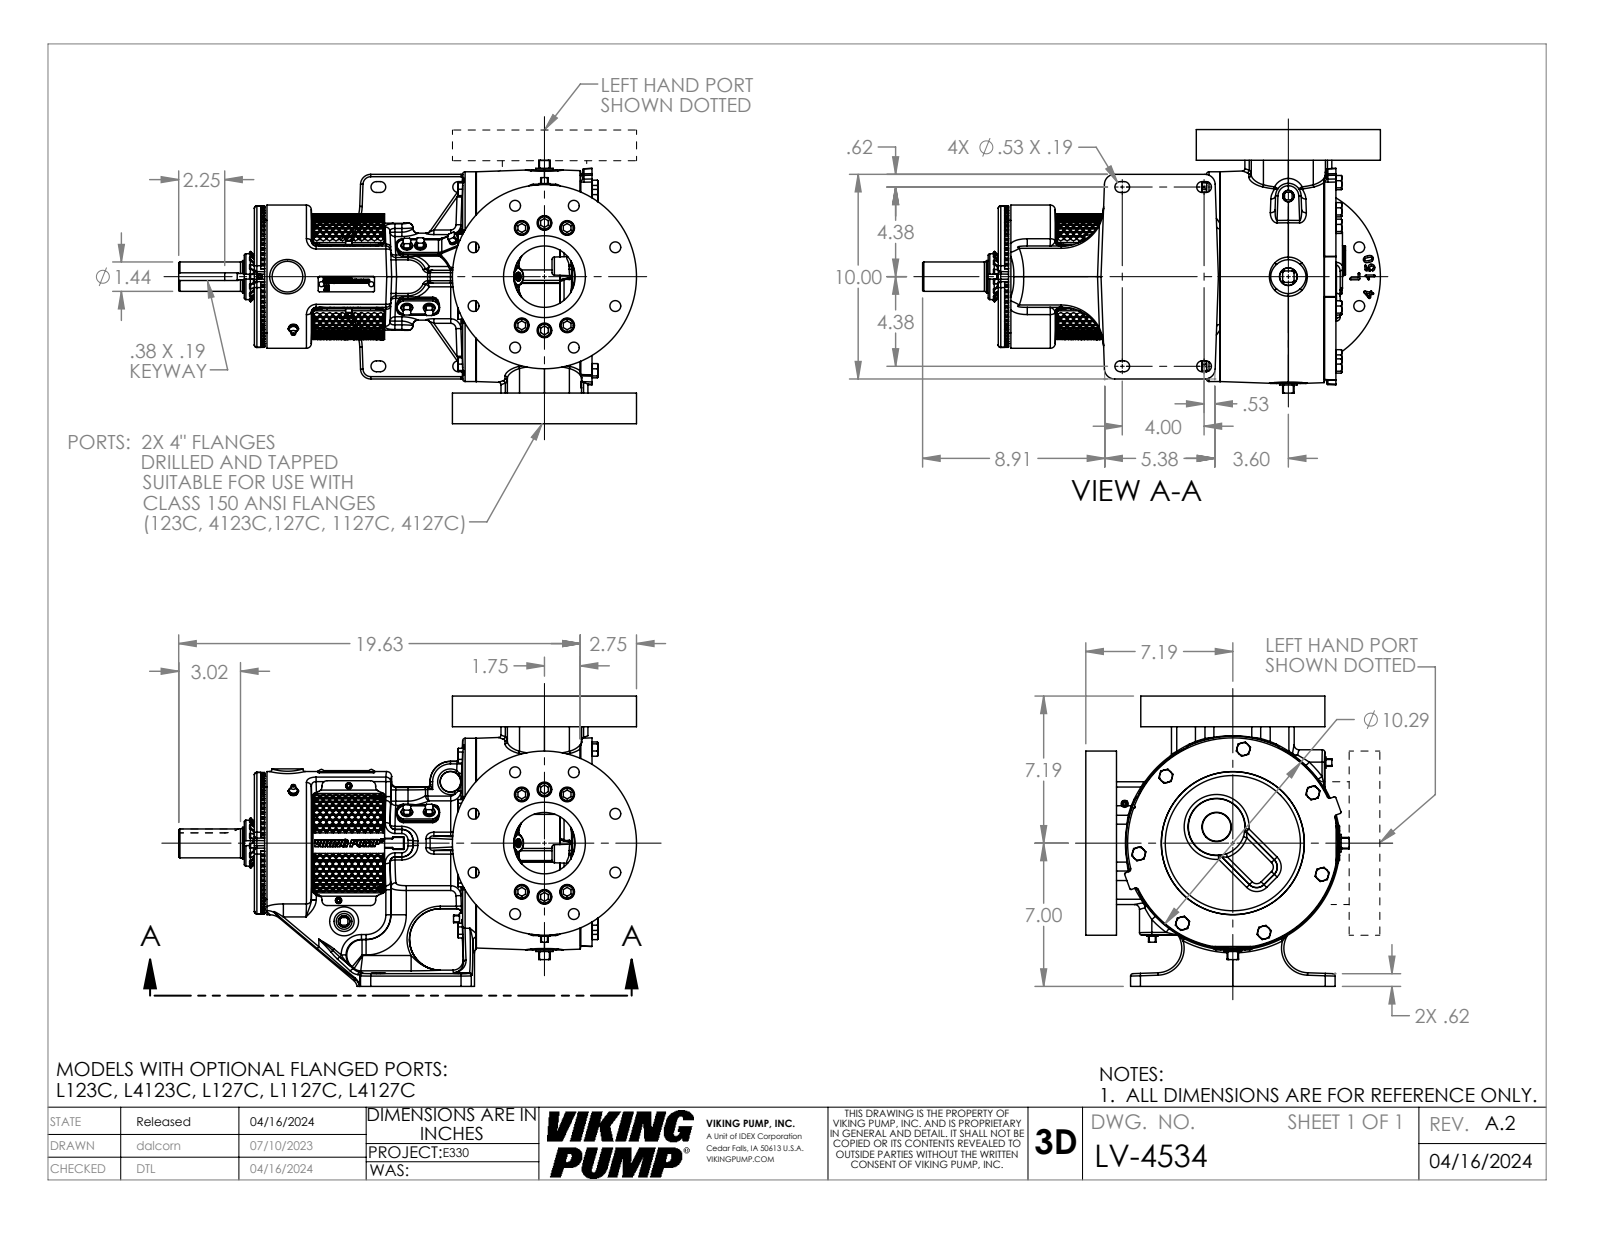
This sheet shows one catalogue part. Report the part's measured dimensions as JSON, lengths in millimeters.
{"part_name": "LV-4534", "step_written_by": "SolidWorks 2022 (AUTOMOTIVE_DESIGN)", "units": "millimeters", "bodies": {"solids": 1, "faces": 4460, "planar": 1526, "cylindrical": 968, "other": 1966}, "overall_size": [568.5, 360.4, 327.1], "volume_mm3": 16130000, "surface_area_mm2": 950300, "round_holes": [[13.5, 16], [11.9, 12], [18.3, 12], [27.8, 8], [5.1, 6], [6.4, 6], [4, 3], [6.8, 2], [8, 2], [76.2, 2], [11.5, 1], [40.1, 1]], "round_bosses_or_shafts": [[11.1, 15], [16.8, 12], [15.9, 9], [15.9, 6], [7.9, 3], [228.6, 2], [260.4, 1], [177.8, 1]], "partial_cylinders_radius": [[1.6, 109], [1.8, 74], [3, 74], [6.1, 48], [0.8, 18], [25.4, 16], [12.7, 14], [1.5, 12]], "face_to_face_distances": [38.1, 322.2, 360.3, 6.6, 342.8, 349.4, 12.7, 57.2, 90.1, 252.7], "hole_center_spacings": [72.9, 95.3, 134.7, 176, 76.2, 66.7, 34.9, 28.8]}
